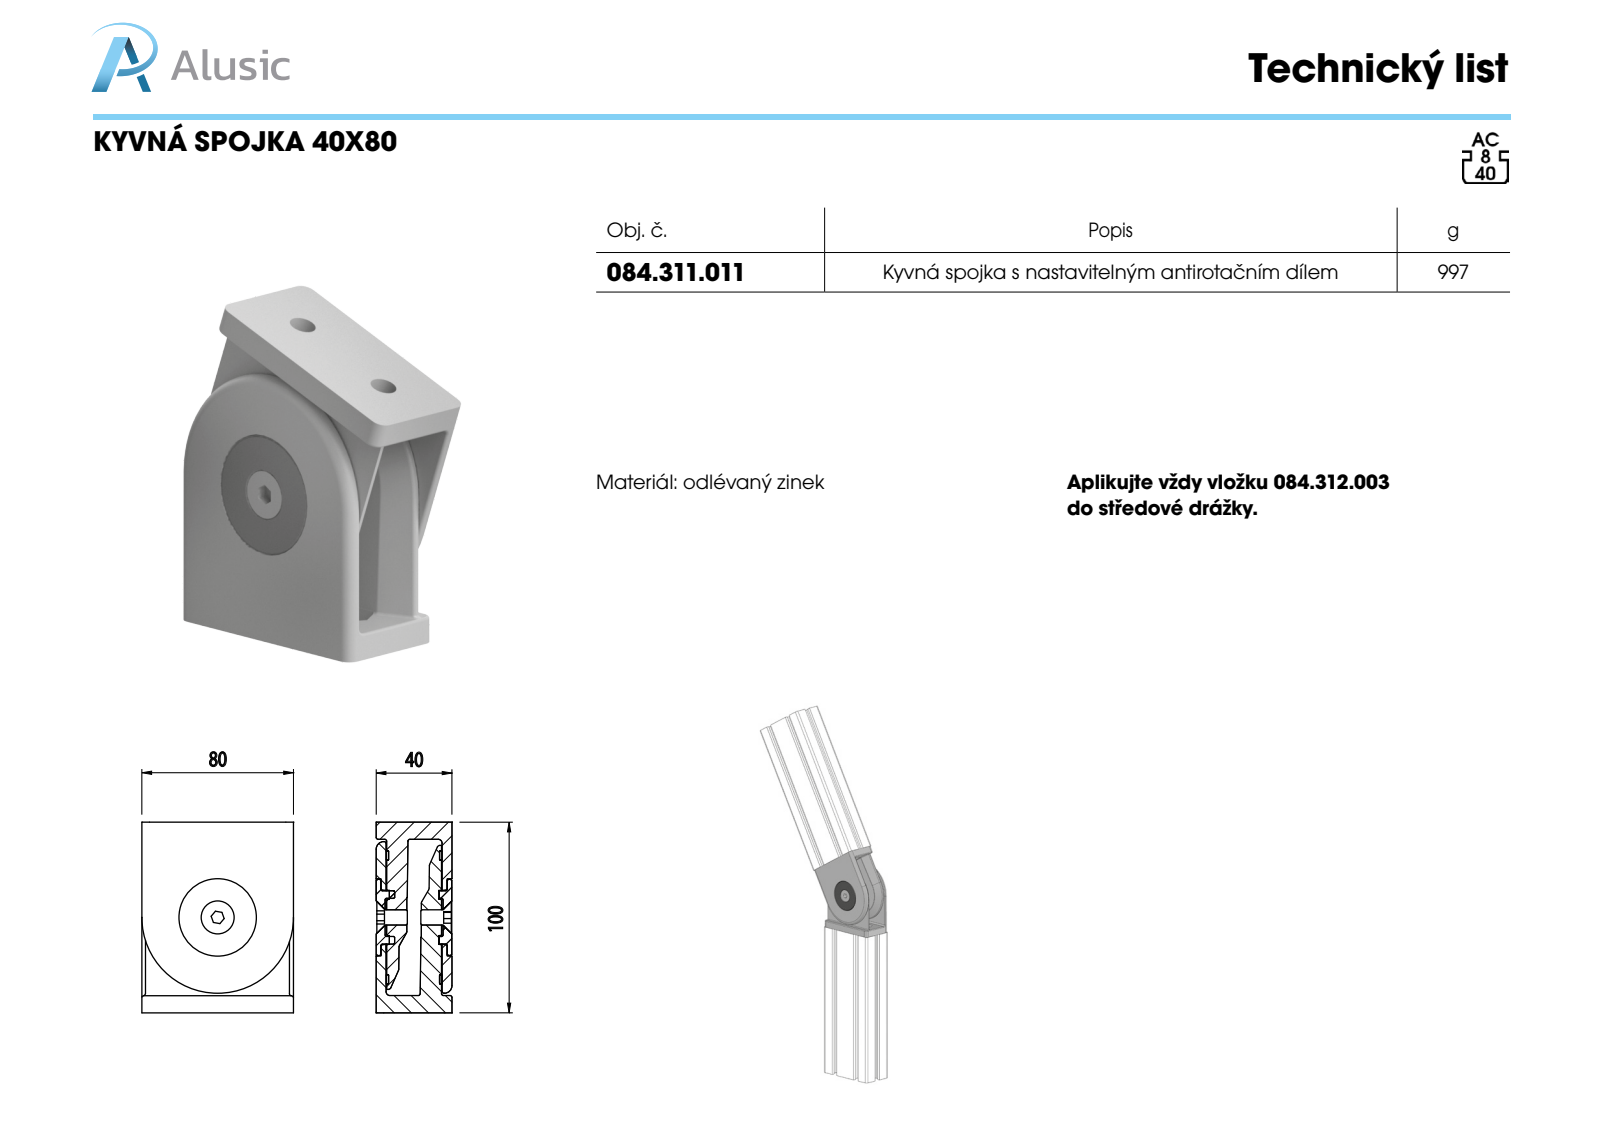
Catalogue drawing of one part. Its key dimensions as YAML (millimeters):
part_name: "084.311.011; 093gr02_093 g r02; 093g4080an; 4din7991m0816e_4din7991m0816e (+3 more)"
step_written_by: "SolidWorks 2011 (CONFIG_CONTROL_DESIGN)"
units: millimeters
bodies: {solids: 12, faces: 900, planar: 260, cylindrical: 340, other: 300}
overall_size: [115.78, 102.43, 39.8]
volume: 179464
surface_area: 79879
round_holes:
  - {diameter: 6.8, count: 1}
  - {diameter: 9, count: 1}
  - {diameter: 20, count: 1}
  - {diameter: 60.4, count: 1}
  - {diameter: 70, count: 1}
round_bosses_or_shafts:
  - {diameter: 2, count: 4}
  - {diameter: 79.6, count: 1}
  - {diameter: 75.6, count: 1}
  - {diameter: 69.6, count: 1}
  - {diameter: 60, count: 1}
  - {diameter: 40, count: 1}
  - {diameter: 28, count: 1}
  - {diameter: 16, count: 1}
partial_cylinders:
  - {radius: 0.2, count: 132}
  - {radius: 1, count: 44}
  - {radius: 4, count: 28}
  - {radius: 2, count: 18}
  - {radius: 1.5, count: 4}
  - {radius: 2.5, count: 4}
  - {radius: 17, count: 1}
  - {radius: 29, count: 1}
face_to_face_distances: [5.2, 34.6, 5.5, 34.3, 29.1, 39.8, 29.4, 34.5, 1, 6.5]
